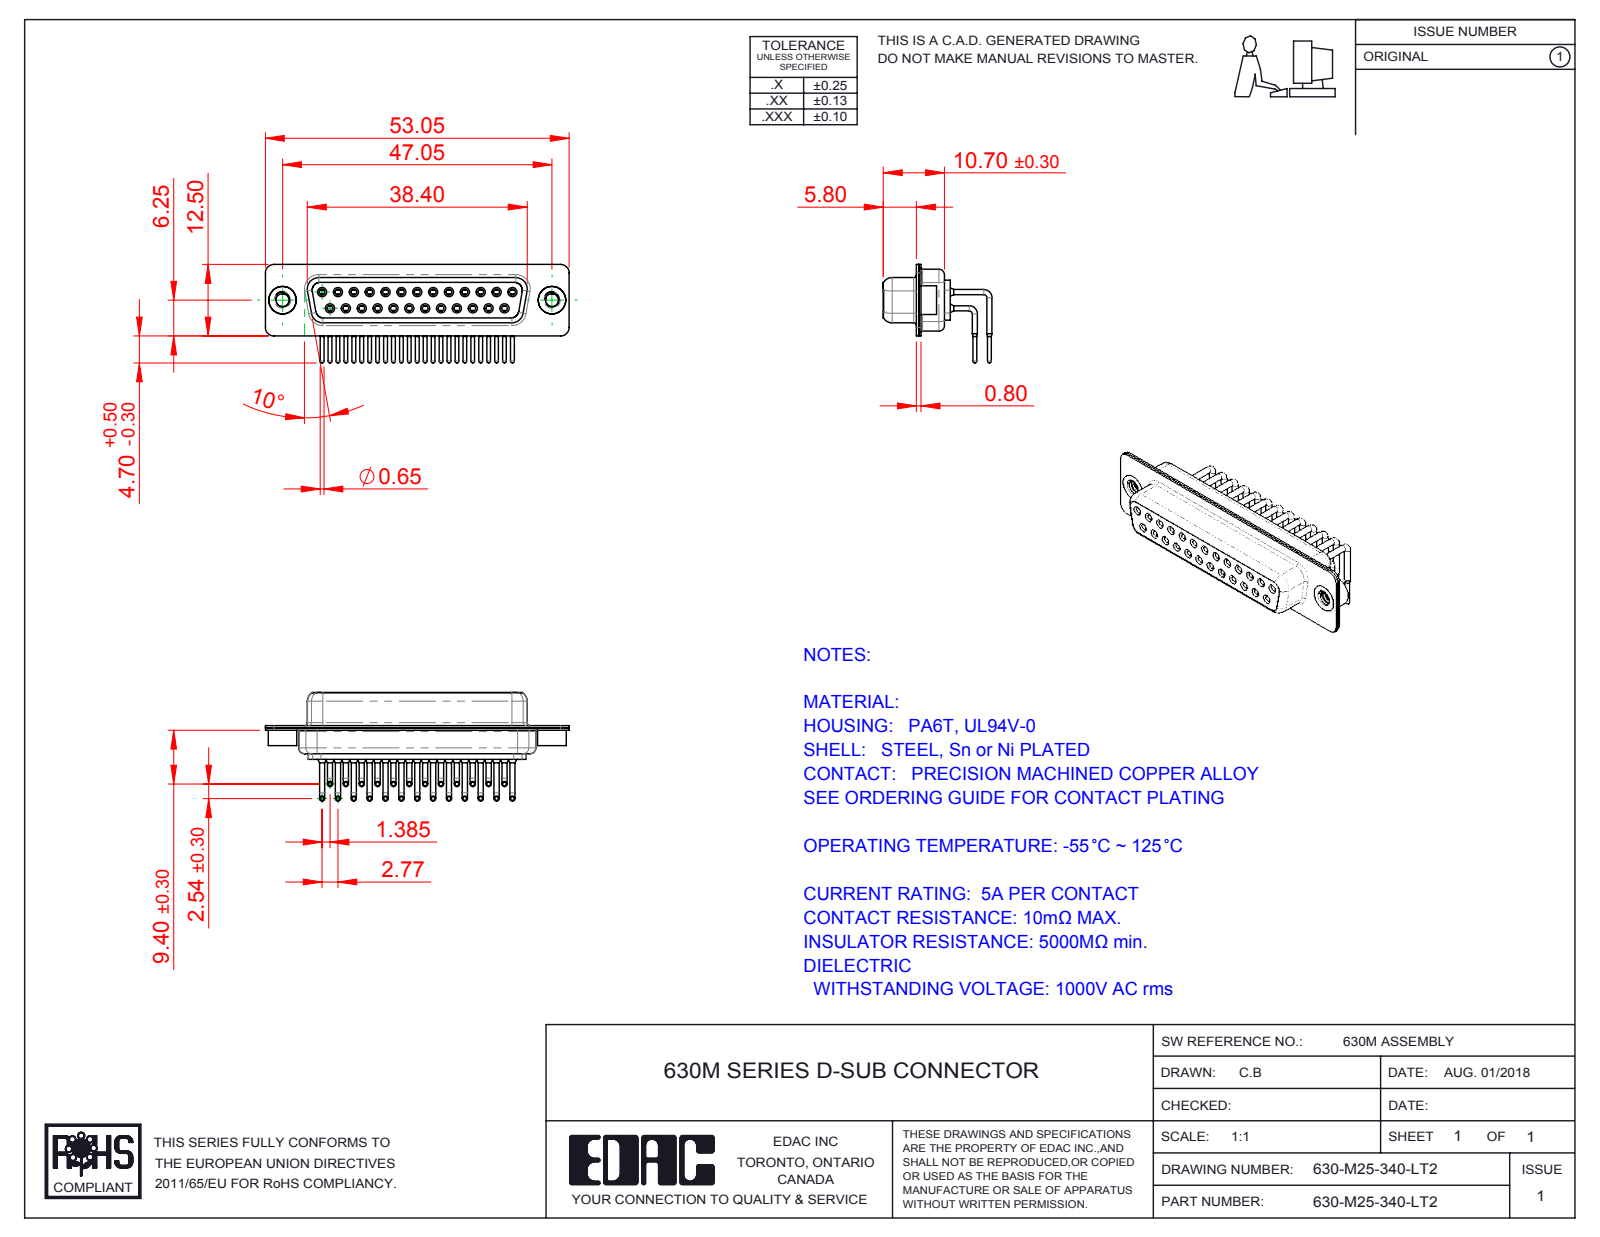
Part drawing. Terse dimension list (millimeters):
name: 630M Housing_25 Contacts; 630-M25-340-LT2; 630M Shell Front_25 Contacts; 630M 4-40 Threaded Rivet (+3 more)
written by: SolidWorks 2016 (CONFIG_CONTROL_DESIGN)
unit: mm
bodies: 30 solids, 1604 faces (442 planar, 712 cylindrical, 450 other)
size: 53.05 × 18.99 × 17.2
volume: 3 898 mm³; area: 9 728 mm²
holes: 25× ⌀1, 25× ⌀1.1, 25× ⌀1.7, 25× ⌀1.8, 25× ⌀2, 2× ⌀2.26, 2× ⌀4, 2× ⌀4.8
bosses: 50× ⌀0.9, 25× ⌀1.6, 25× ⌀1.5, 25× ⌀0.65, 2× ⌀5, 2× ⌀4.9
rounds: 16× R1.5, 12× R2, 10× R1.35, 8× R1.6, 4× R0.25, 4× R0.5, 4× R0.6, 4× R0.65
face distances: 0.4, 1.45, 8.95, 6.2, 2.3, 1.9, 8.5, 7.05, 0.45, 0.85
hole spacings: 3.16, 2.77, 5.54, 8.31, 11.08, 13.85, 5.04, 7.49
